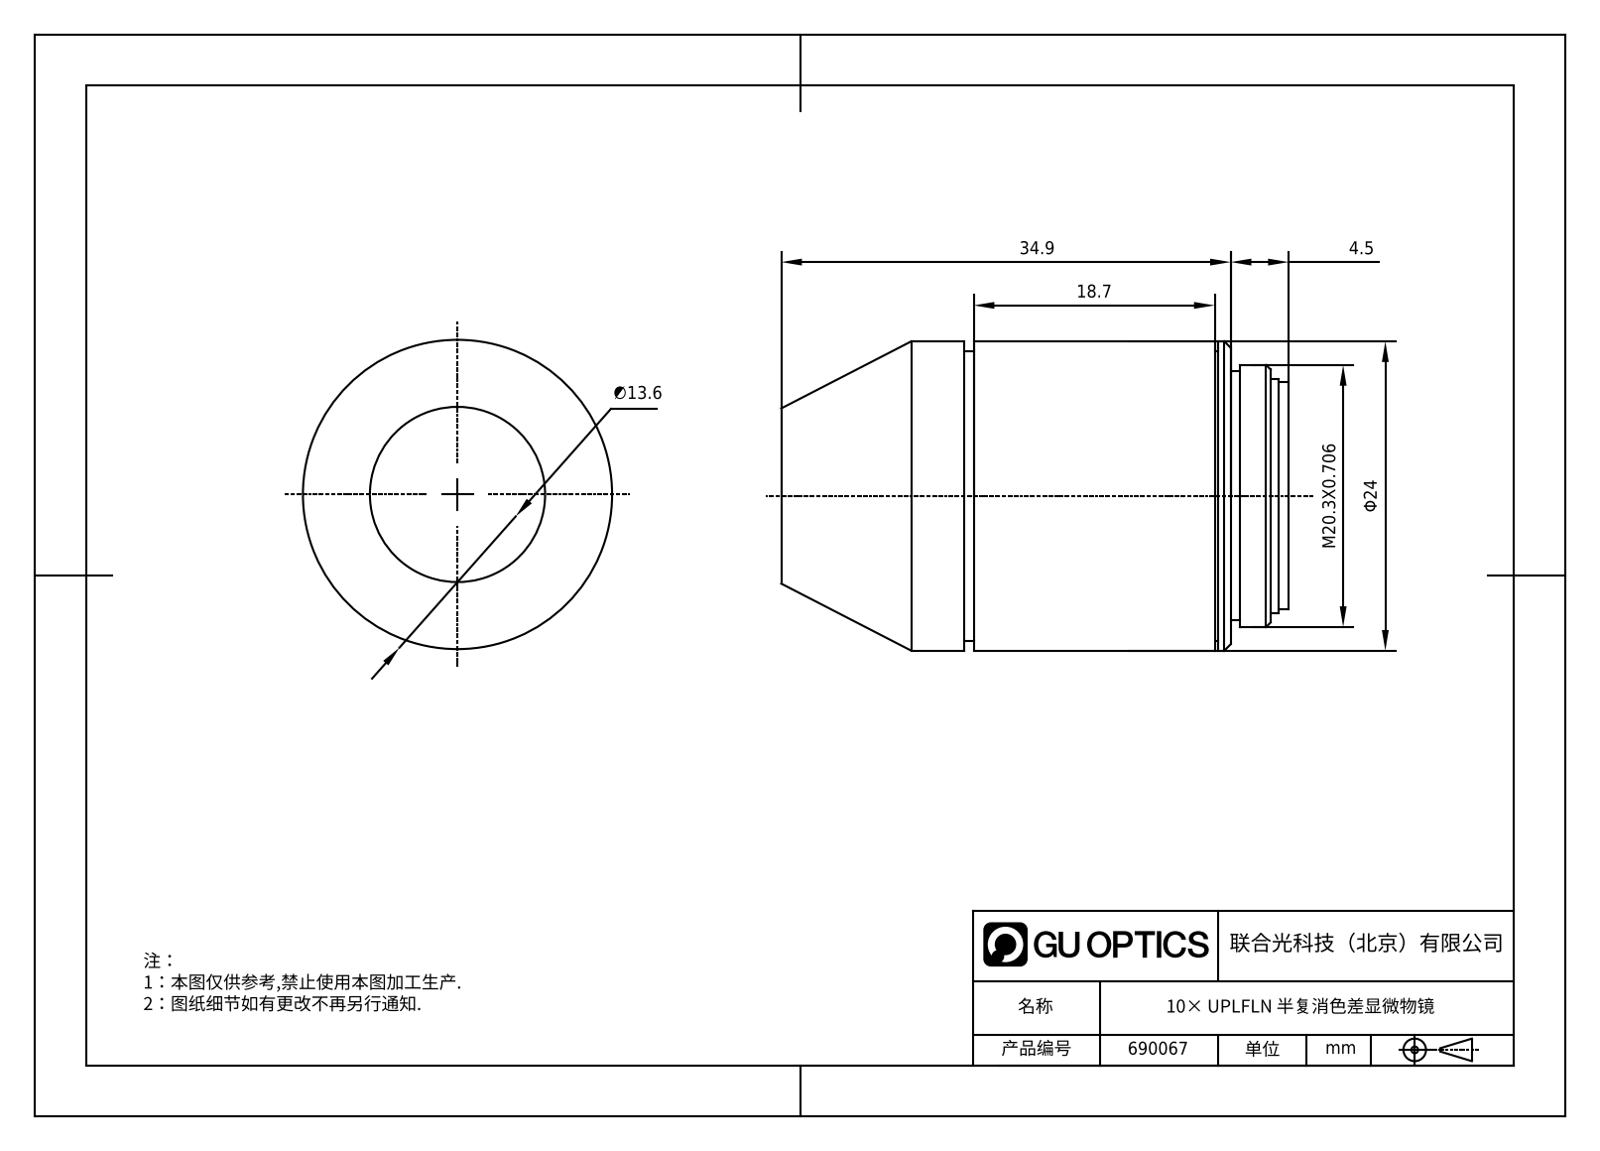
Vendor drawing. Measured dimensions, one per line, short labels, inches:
name: 690067
written by: SolidWorks 2020 (CONFIG_CONTROL_DESIGN)
unit: in
bodies: 1 solid, 34 faces (10 planar, 18 cylindrical, 6 other)
size: 1.551 × 0.945 × 0.945
volume: 0.937 in³; area: 5.662 in²
bosses: 1× ⌀0.945, 1× ⌀0.886, 1× ⌀0.8, 1× ⌀0.761, 1× ⌀0.713, 1× ⌀0.694
face distances: 1.551, 1.374, 0.177, 0.815, 0.03, 0.559, 1.324, 0.766, 0.992, 0.049
